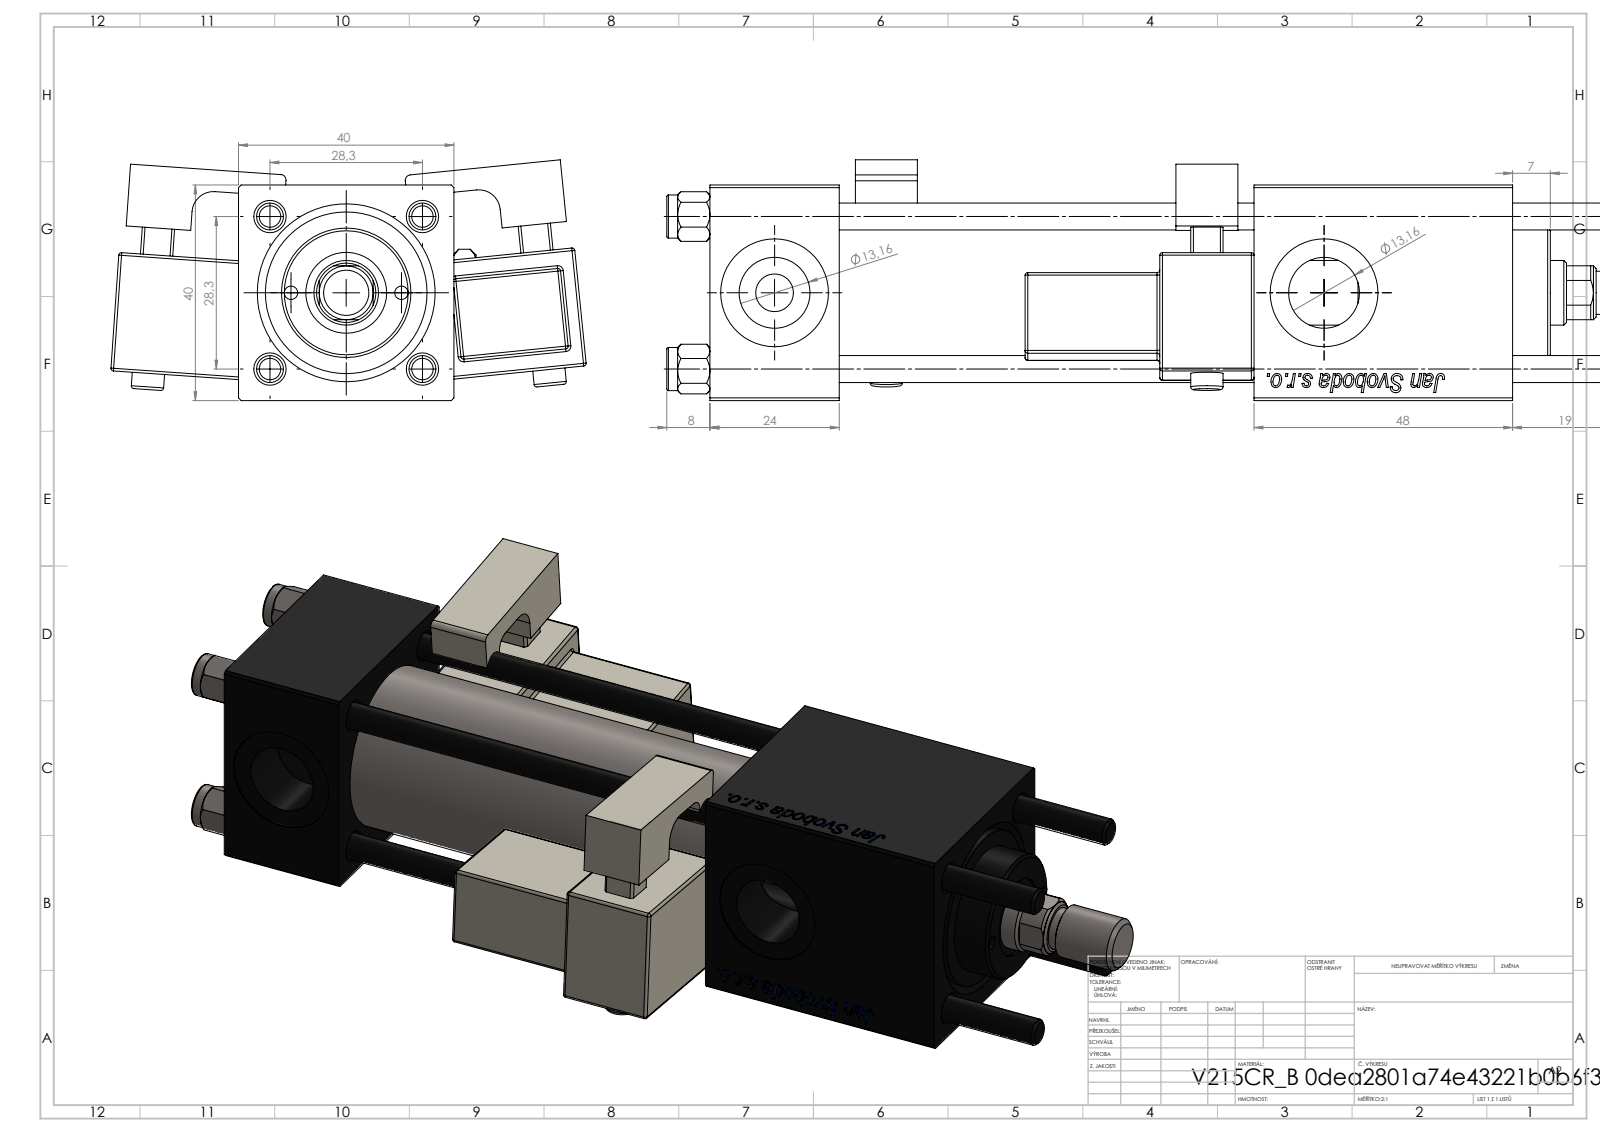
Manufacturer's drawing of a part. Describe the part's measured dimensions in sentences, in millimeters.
The part is named "NUT_M5_B; V215CR_B-1; Zatka_pro_OIL_PORT; V215_VC_A (+4 more)". Its 3-D file was written by "SolidWorks 2019 (CONFIG_CONTROL_DESIGN)". It is 15 solids with 1386 faces: 520 planar, 154 cylindrical and 712 other. Overall it measures 186 by 88.2 by 44.67 millimeters. Its volume is 199 277 cubic millimeters and its surface area 80 695 square millimeters. Round holes: 4 of diameter 5, 3 of diameter 20, 2 of diameter 2.5, 2 of diameter 7, 2 of diameter 13.16, 1 of diameter 6.5, 1 of diameter 12, 1 of diameter 15, 1 of diameter 25, 1 of diameter 30. Round bosses or shafts: 5 of diameter 8, 2 of diameter 6, 1 of diameter 31, 1 of diameter 24, 1 of diameter 10. Partial cylindrical surfaces (rounded edges, fillets, slot ends): 48 of radius 0.5, 2 of radius 1, 2 of radius 2.5, 2 of radius 4, 1 of radius 5.5. The main face-to-face distances are 40, 3, 24, 77, 101, 18.51, 20, 48, 23, 120.3. The hole center spacings are 14.68, 20.01, 28.21, 28.3, 10.25, 40.02, 20.5, 102.
